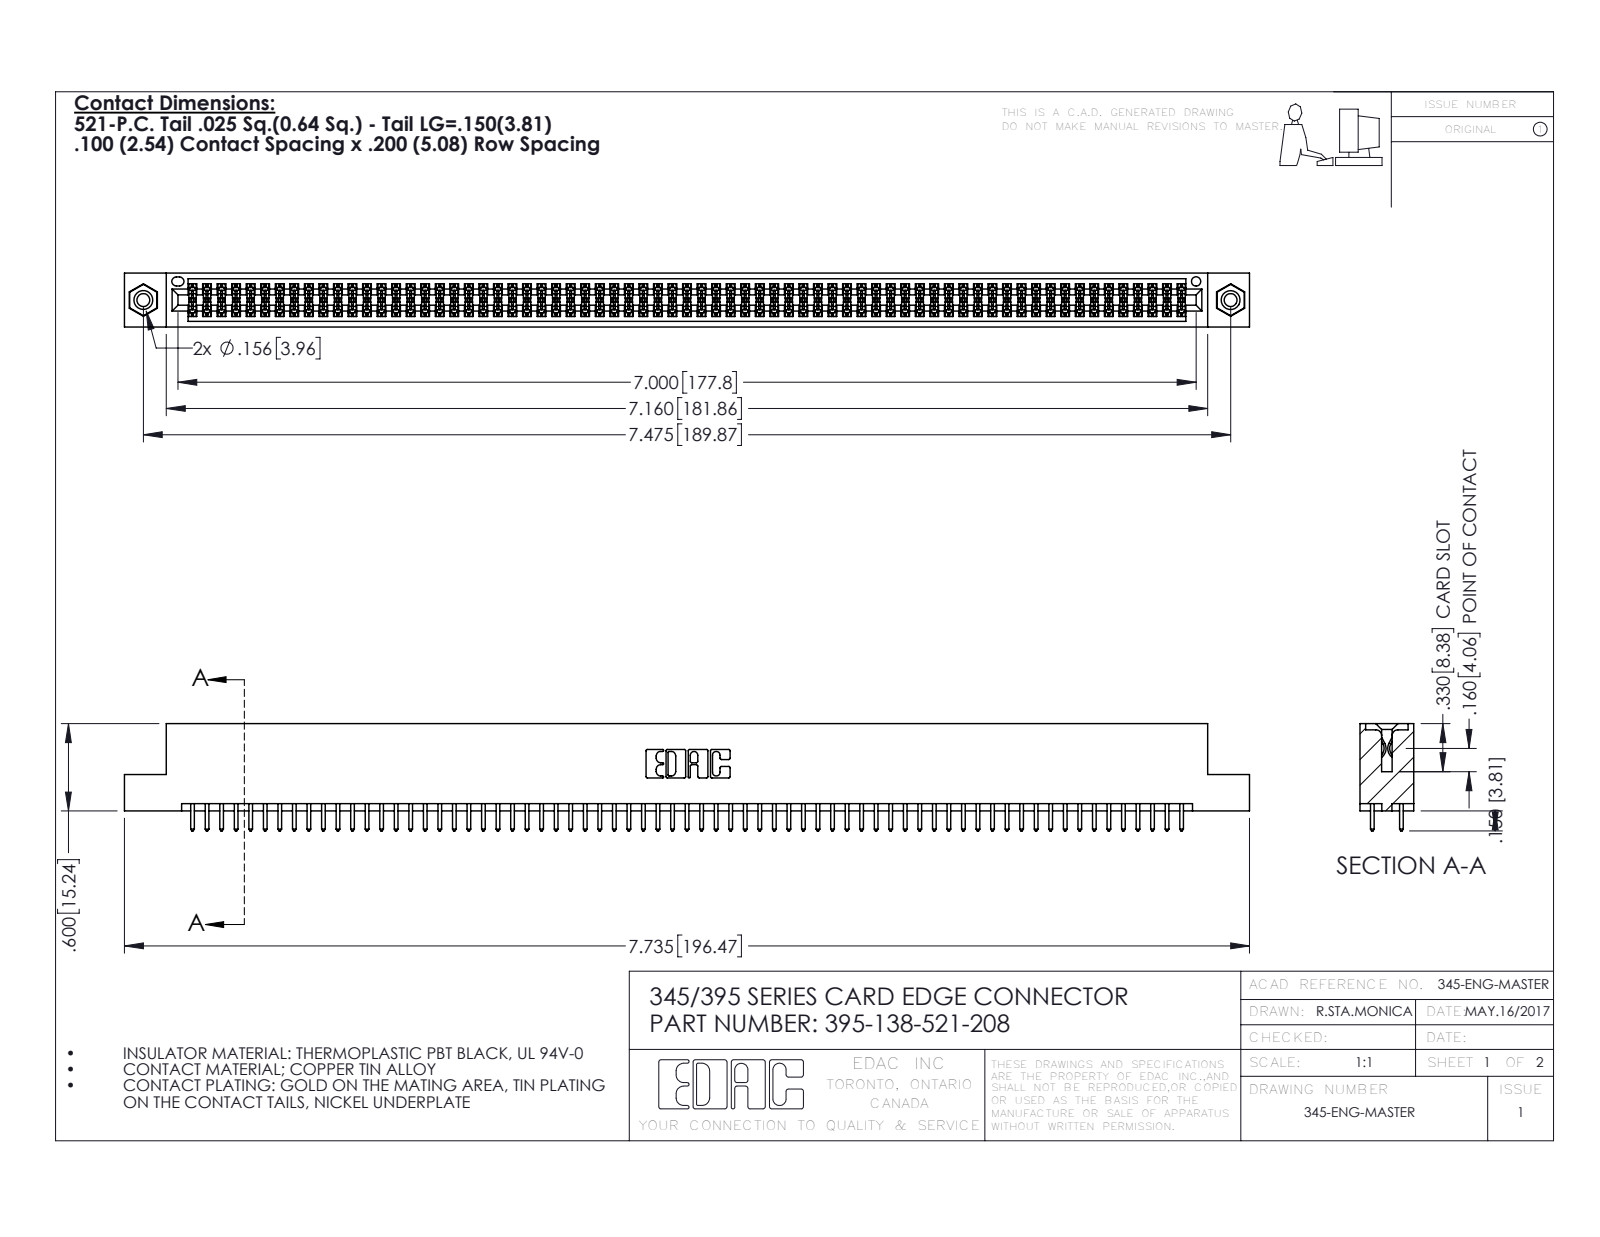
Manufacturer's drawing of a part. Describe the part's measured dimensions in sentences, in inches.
The part is named "345-292-001_345-293-121; 345-250-001_345-250-003-102; 345 Part_Flush Mounting Lugs - 0.156 Dia-TI; 395-138-521-208". Its 3-D file was written by "SolidWorks 2016 (CONFIG_CONTROL_DESIGN)". It is 141 solids with 7086 faces: 4666 planar, 2404 cylindrical and 16 other. Overall it measures 7.735 by 0.737 by 0.37 inches. Its volume is 1.176 cubic inches and its surface area 44.42 square inches. Round holes: 2 of diameter 0.089, 2 of diameter 0.125, 2 of diameter 0.156, 1 of diameter 0.064. Round bosses or shafts: 2 of diameter 0.155. Partial cylindrical surfaces (rounded edges, fillets, slot ends): 207 of radius 0.006, 138 of radius 0.01, 22 of radius 0.01, 6 of radius 0.007, 6 of radius 0.031, 3 of radius 0.026, 2 of radius 0.014, 2 of radius 0.019. The main face-to-face distances are 0.072, 0.298, 0.2, 0.098, 0.272, 0.025, 0.37, 0.225, 0.175, 0.149. The hole center spacings are 0.27, 7.239, 7.475.
